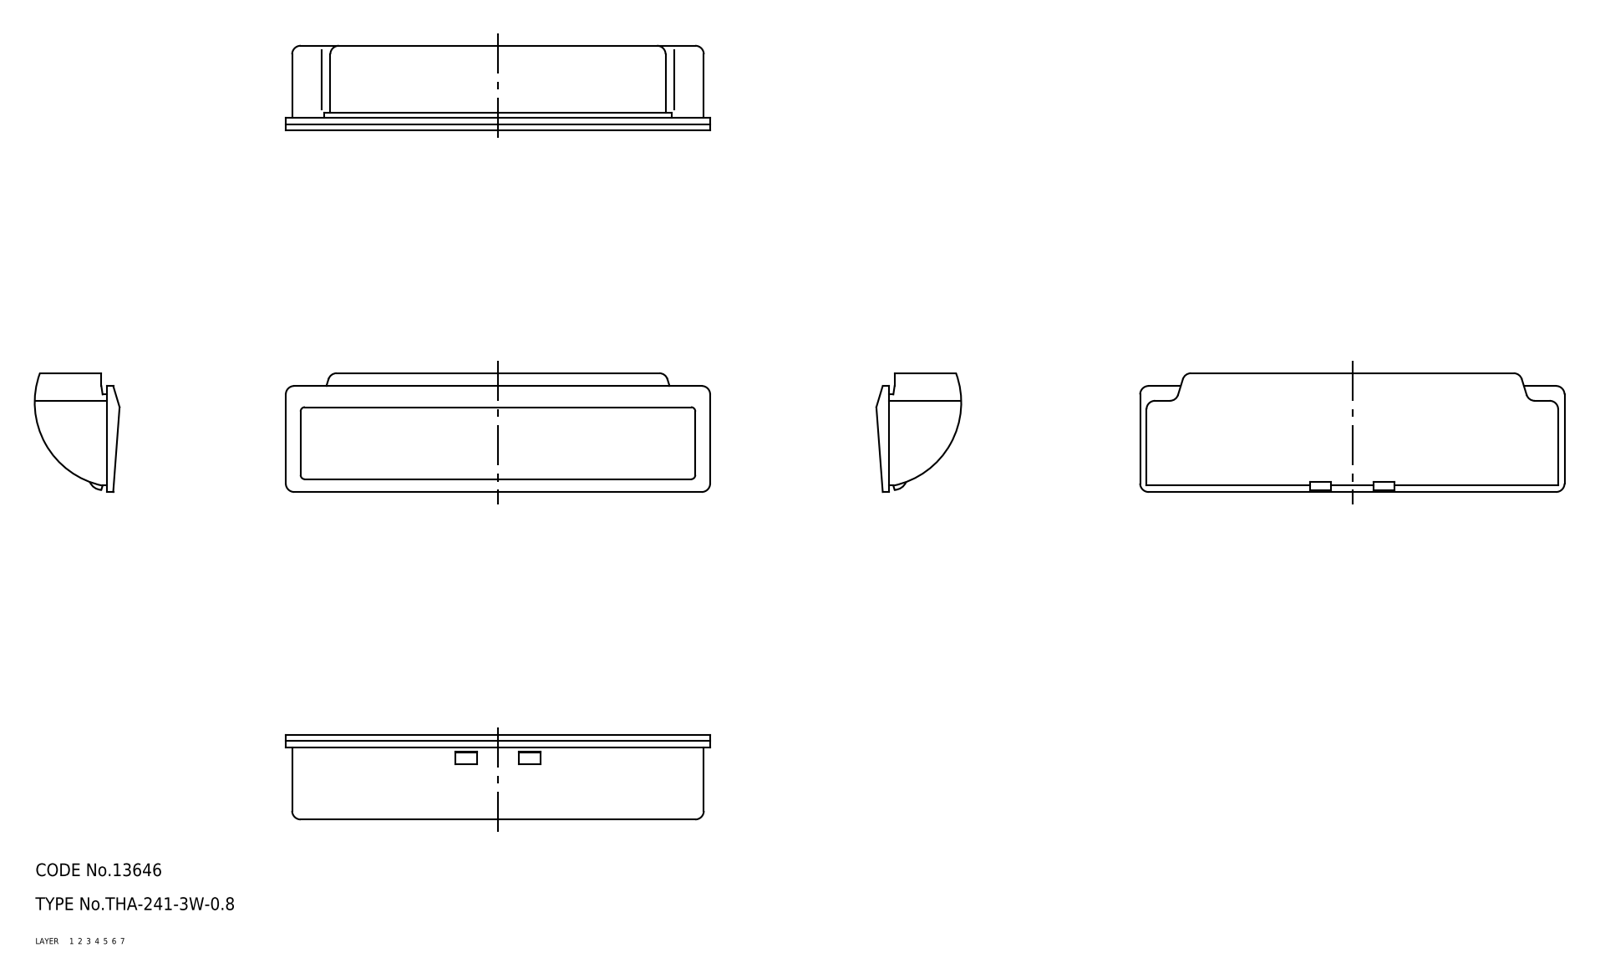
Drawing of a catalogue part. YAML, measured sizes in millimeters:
part_name: "pull; THA_241_3W_0_8"
step_written_by: "SolidWorks 2015 (AUTOMOTIVE_DESIGN)"
units: millimeters
bodies: {solids: 1, faces: 77, planar: 32, cylindrical: 31, other: 14}
overall_size: [100, 28, 20]
volume: 11717
surface_area: 13143
partial_cylinders:
  - {radius: 0.5, count: 12}
  - {radius: 2, count: 11}
  - {radius: 3.5, count: 2}
  - {radius: 3, count: 1}
  - {radius: 18.2, count: 1}
  - {radius: 20, count: 1}
face_to_face_distances: [1.3, 1.5, 2, 95, 6.7, 8, 20, 3, 5, 97]
